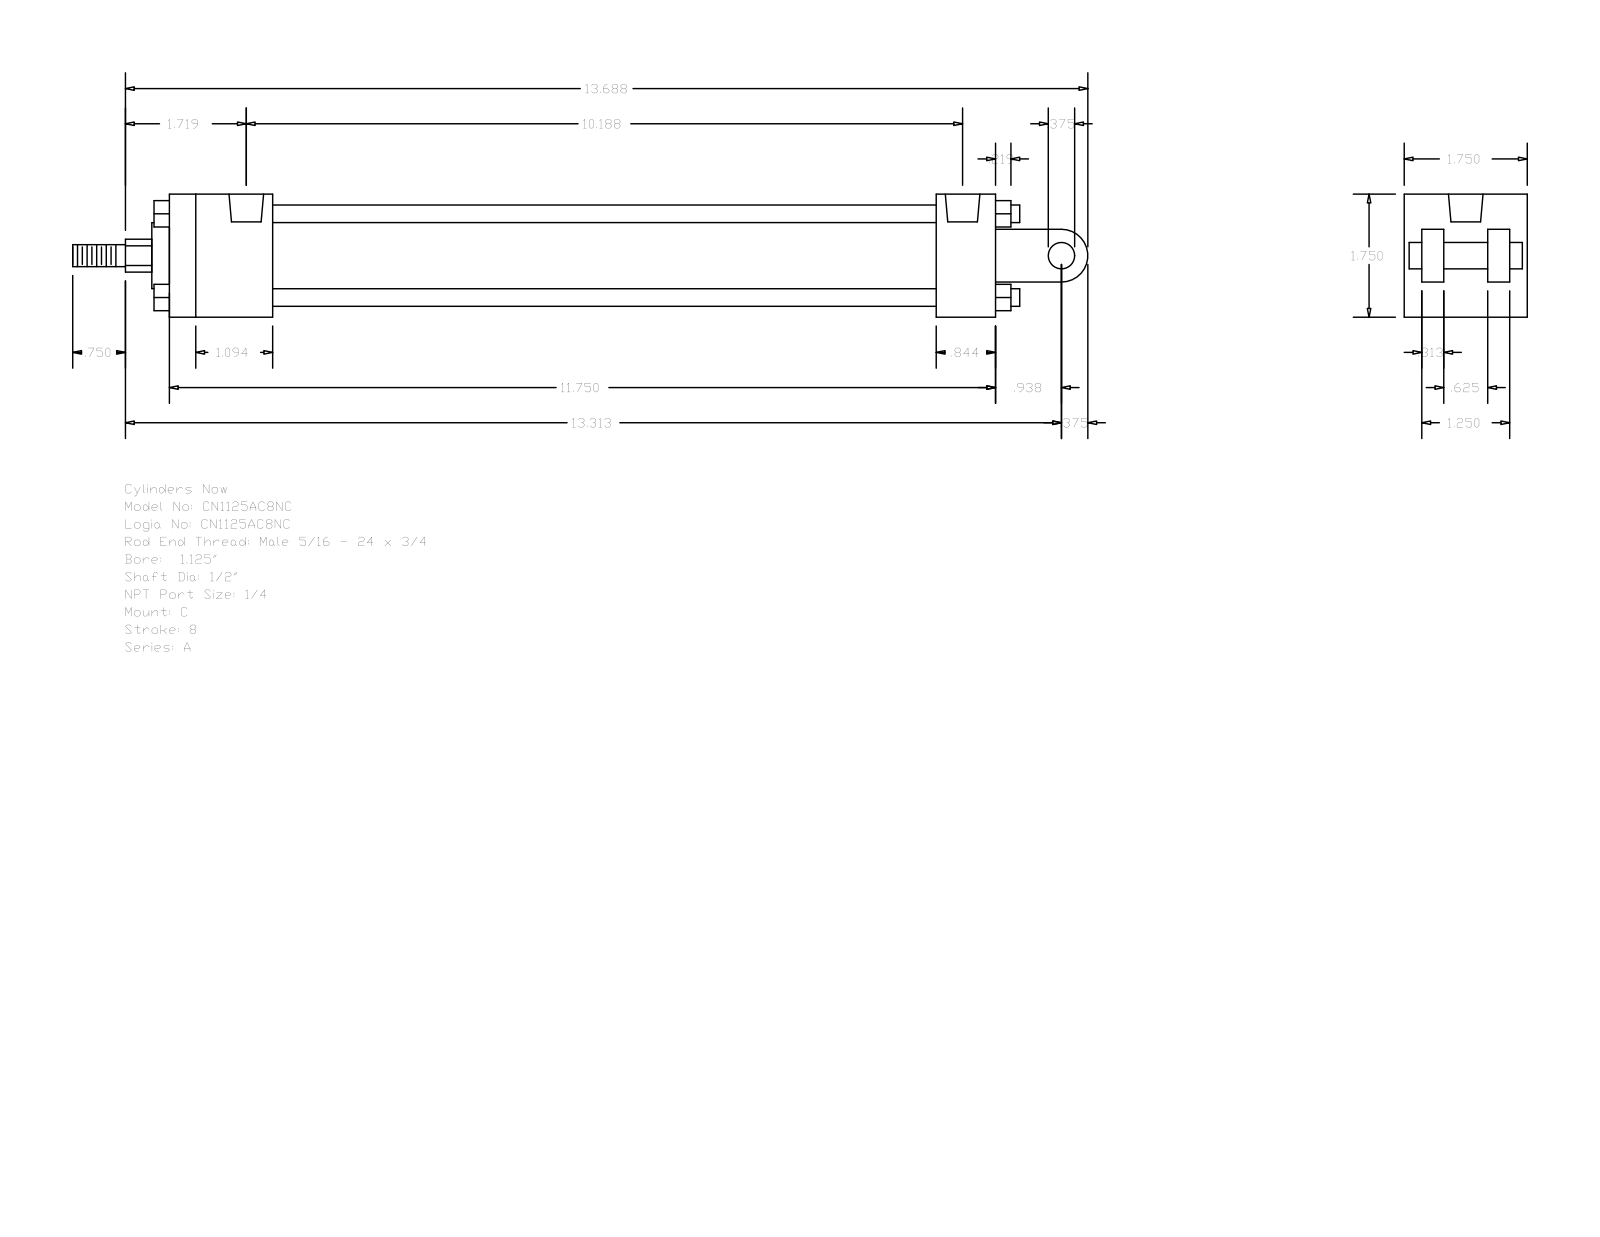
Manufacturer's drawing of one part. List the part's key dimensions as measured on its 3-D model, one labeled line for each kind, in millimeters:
Part name (STEP PRODUCT): A_C__0112_0.5
STEP written by: GSSL Pune (CONFIG_CONTROL_DESIGN)
Units: millimetres
Bodies: 0 solids, 135 faces (102 planar, 33 cylindrical, 0 other)
Overall size (bounding box): 366.71 × 44.45 × 44.45
Round holes (diameter × count): ⌀5.56 ×4, ⌀12.49 ×2
Round bosses / shafts (diameter × count): ⌀6.35 ×4, ⌀31.88 ×1, ⌀23.81 ×1, ⌀12.7 ×1, ⌀9.53 ×1, ⌀7.94 ×1
Partial cylindrical surfaces — rounded edges, fillets, slot ends (radius × count): R5.94 ×1, R9.53 ×1
Main face-to-face distances: 44.46, 6.35, 31.76, 14.29, 298.44, 30.17, 277.01, 21.43, 37.3, 239.71
Hole centre spacings: 255.59, 1.58, 1.59, 257.17, 257.18, 258.76
